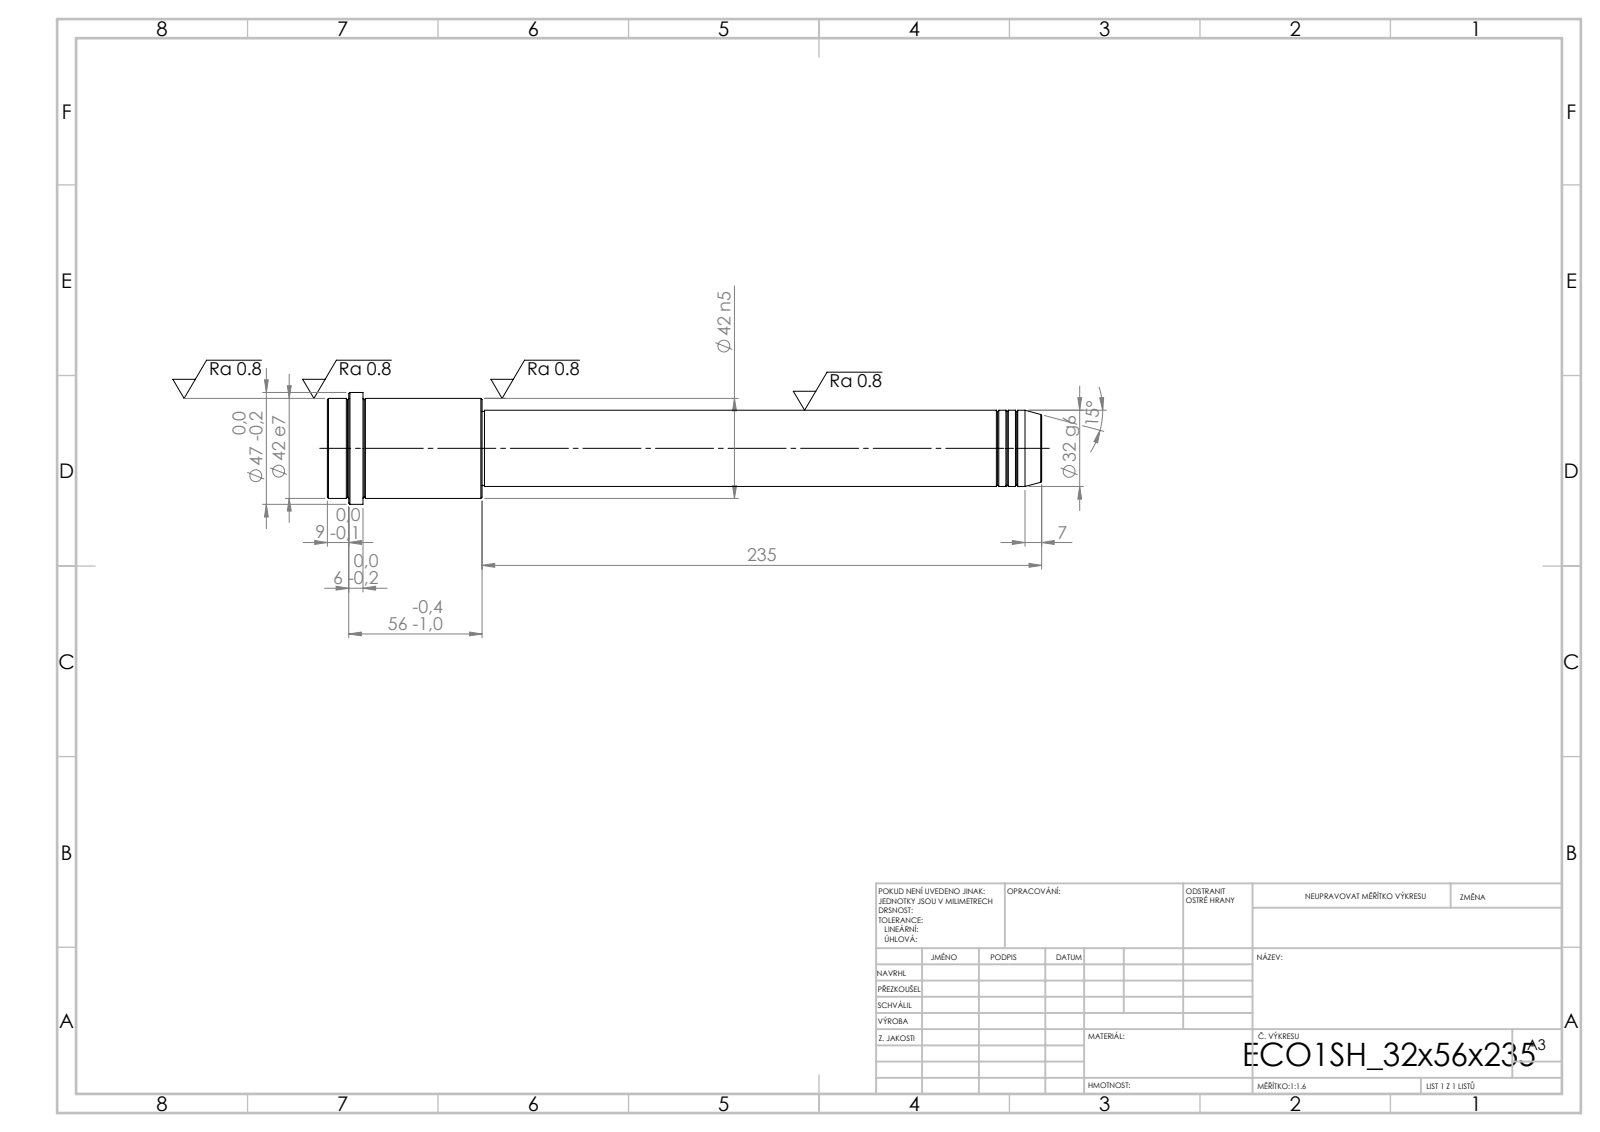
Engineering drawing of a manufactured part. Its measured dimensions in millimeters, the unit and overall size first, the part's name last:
Units: millimetres
Overall size (bounding box): 300 × 47 × 47
Round bosses / shafts (diameter × count): ⌀47 ×1, ⌀42 ×1, ⌀32 ×1, ⌀31 ×1
Main face-to-face distances: 300, 235, 65, 285, 50, 15, 291, 56, 6, 9
Volume: 280 192 mm³ · Surface area: 35 841 mm²
Bodies: 1 solid, 52 faces (6 planar, 16 cylindrical, 30 other)
STEP written by: SolidWorks 2019 (CONFIG_CONTROL_DESIGN)
